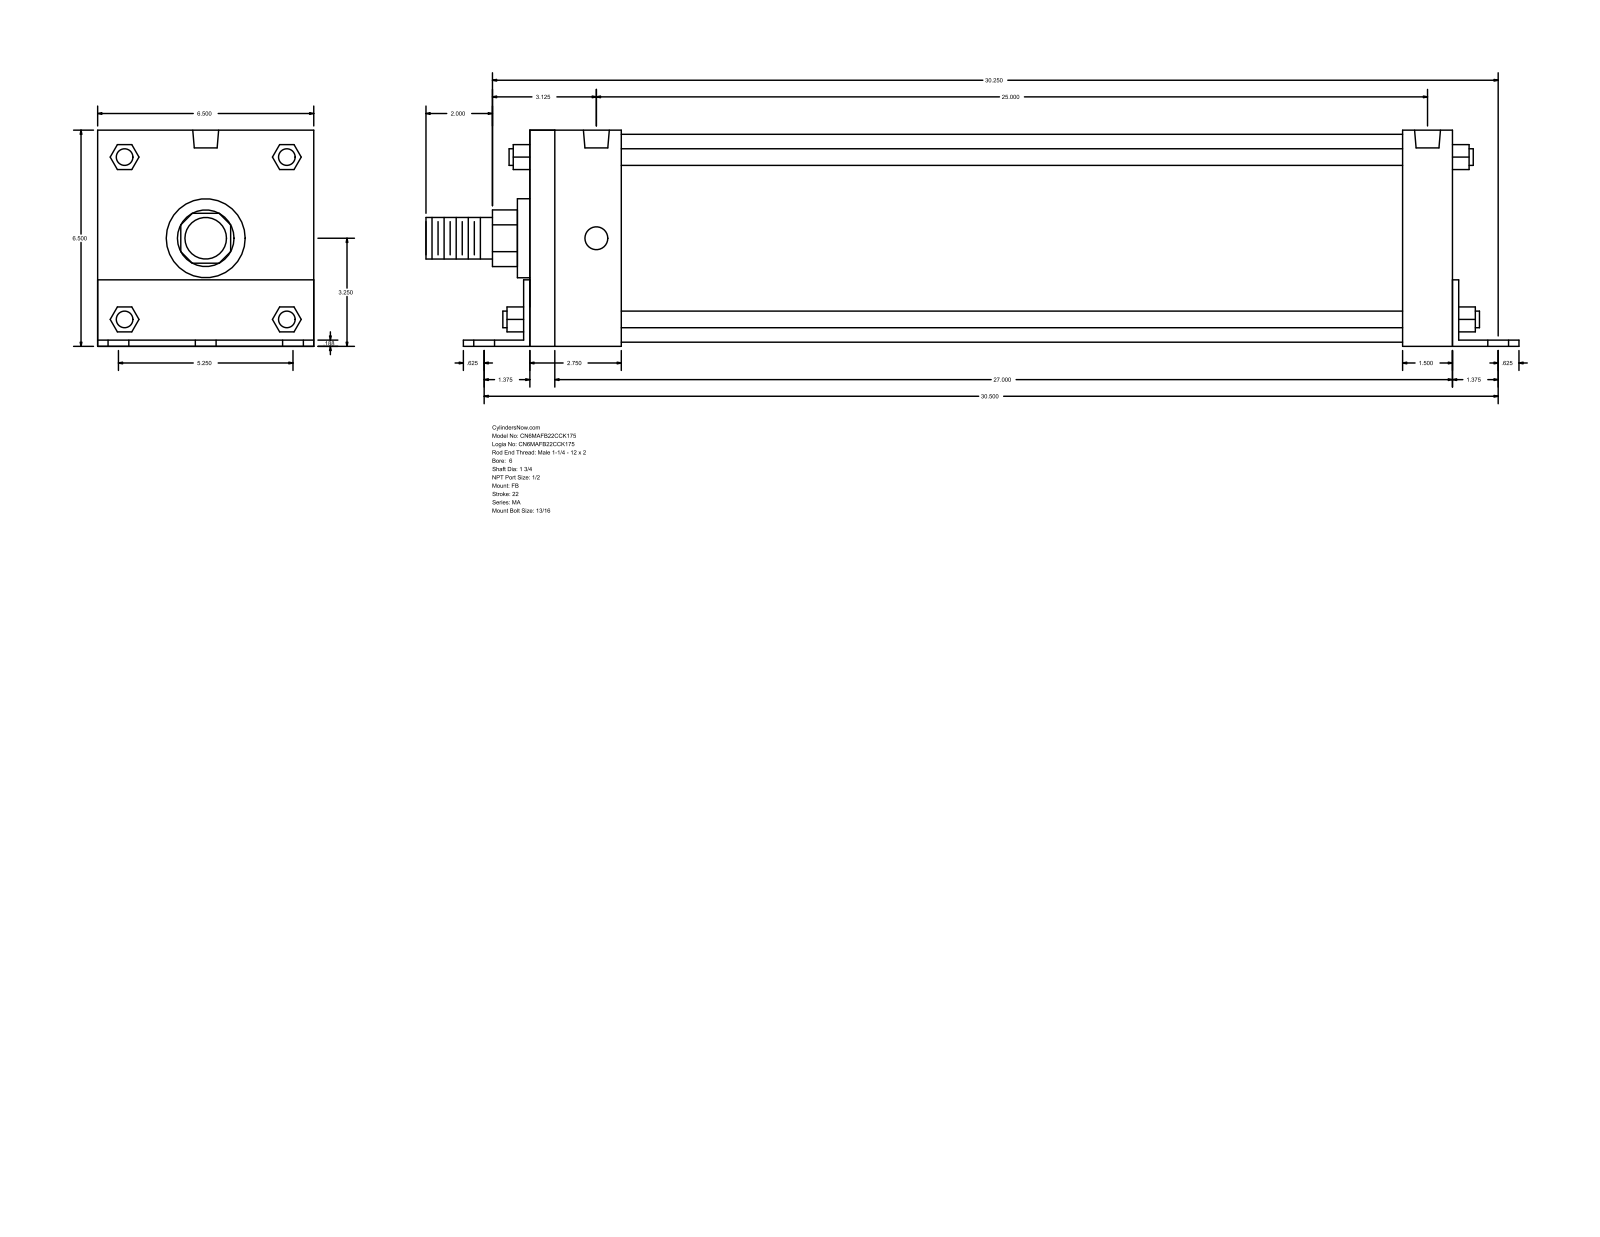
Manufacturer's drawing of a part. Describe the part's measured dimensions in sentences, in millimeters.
The part is named "MA_FB__0600_1.75". Its 3-D file was written by "GSSL Pune (CONFIG_CONTROL_DESIGN)". It is 0 solids with 140 faces: 105 planar, 35 cylindrical and 0 other. Overall it measures 835.02 by 165.15 by 165.1 millimeters. Round holes: 6 of diameter 20.64, 4 of diameter 17.46, 2 of diameter 19.77. Round bosses or shafts: 4 of diameter 12.7, 1 of diameter 158.75, 1 of diameter 60.33, 1 of diameter 44.45, 1 of diameter 31.75. Partial cylindrical surfaces (rounded edges, fillets, slot ends): 1 of radius 21.63, 1 of radius 32.05. The main face-to-face distances are 165.1, 4.76, 704.85, 165.15, 4.71, 160.39, 69.85, 74.61, 4.77, 709.62. The hole center spacings are 66.67, 777.56, 774.7, 85.78, 108.6, 133.34, 635, 692.19.
